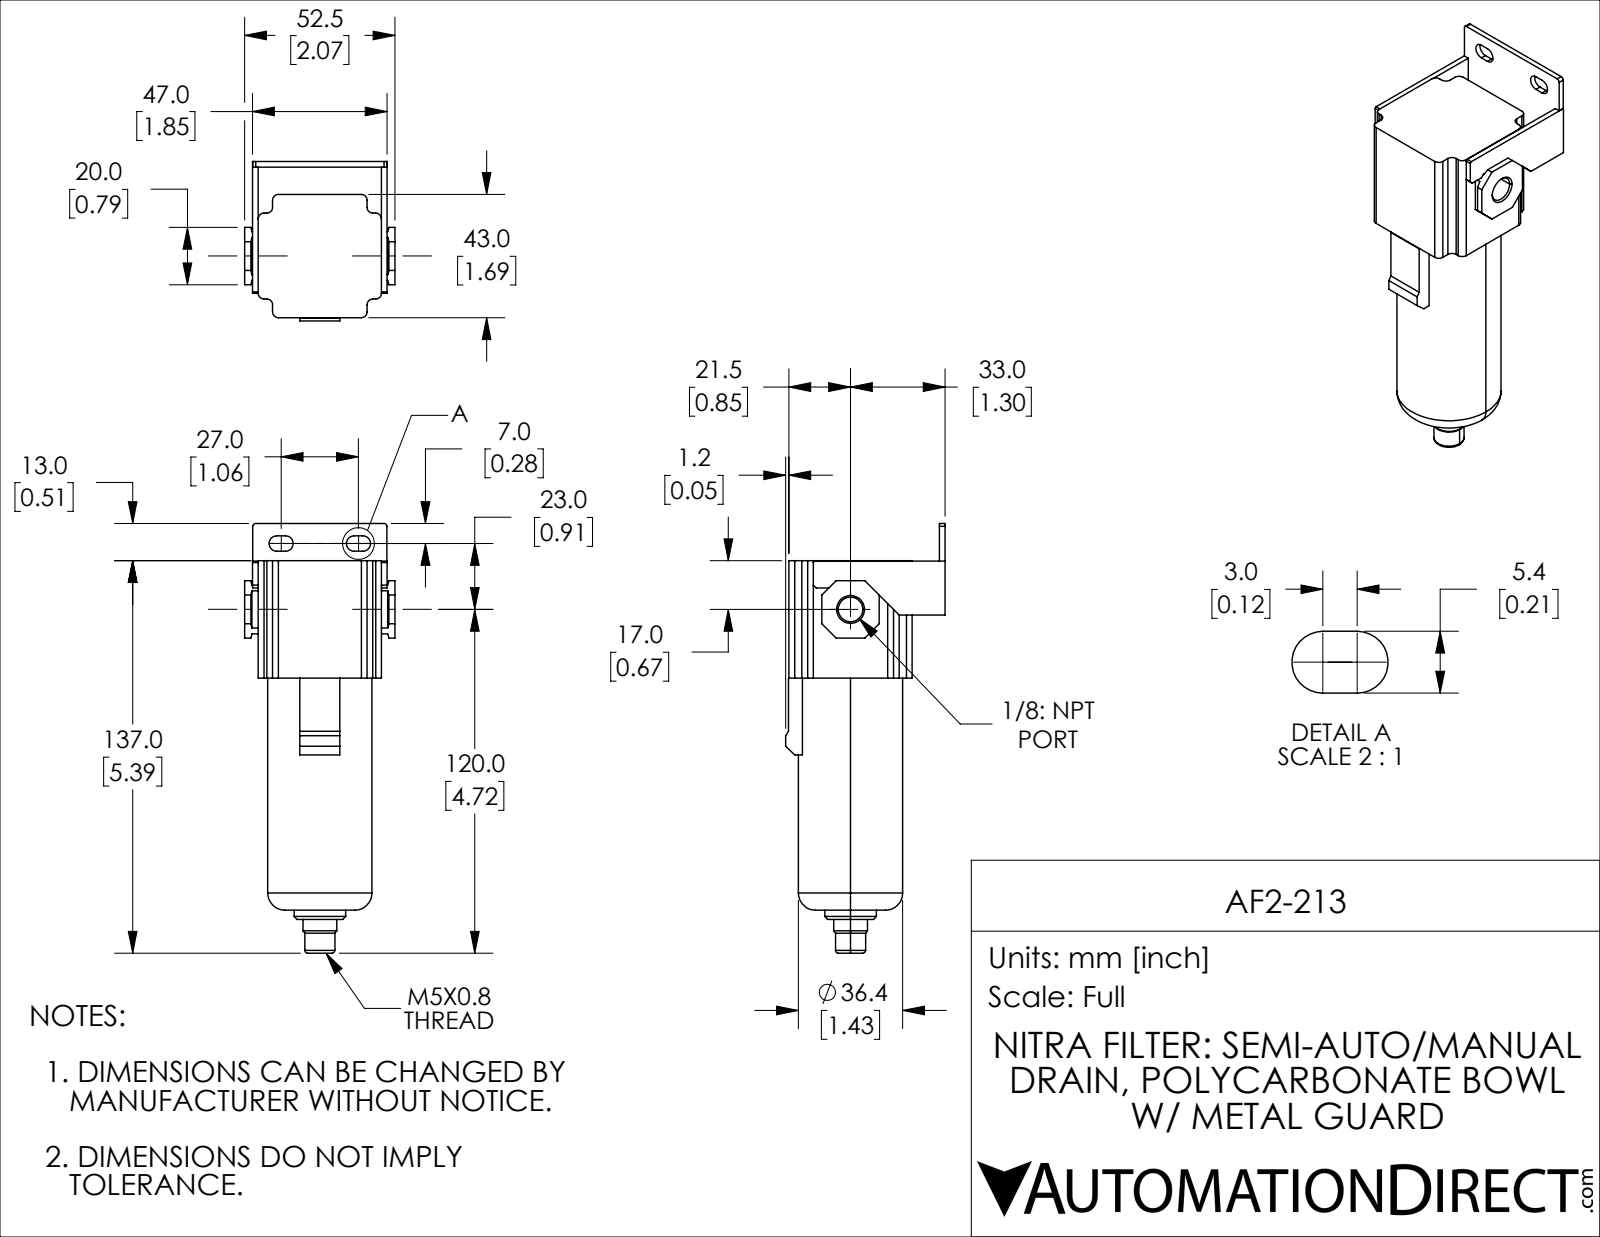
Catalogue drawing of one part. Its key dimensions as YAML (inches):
part_name: "AF2-213"
step_written_by: "SolidWorks 2019 (CONFIG_CONTROL_DESIGN)"
units: inches
bodies: {solids: 1, faces: 136, planar: 90, cylindrical: 32, other: 14}
overall_size: [5.906, 2.192, 2.067]
volume: 10.02
surface_area: 40.34
round_holes:
  - {diameter: 0.163, count: 1}
  - {diameter: 0.337, count: 1}
round_bosses_or_shafts:
  - {diameter: 1.433, count: 1}
  - {diameter: 0.709, count: 1}
  - {diameter: 0.465, count: 1}
  - {diameter: 0.413, count: 1}
partial_cylinders:
  - {radius: 0.079, count: 12}
  - {radius: 0.106, count: 4}
  - {radius: 0.039, count: 2}
face_to_face_distances: [0.079, 1.693, 0.374, 2.067, 0.453, 1.772, 2.146, 1.614, 1.85, 0.108]
